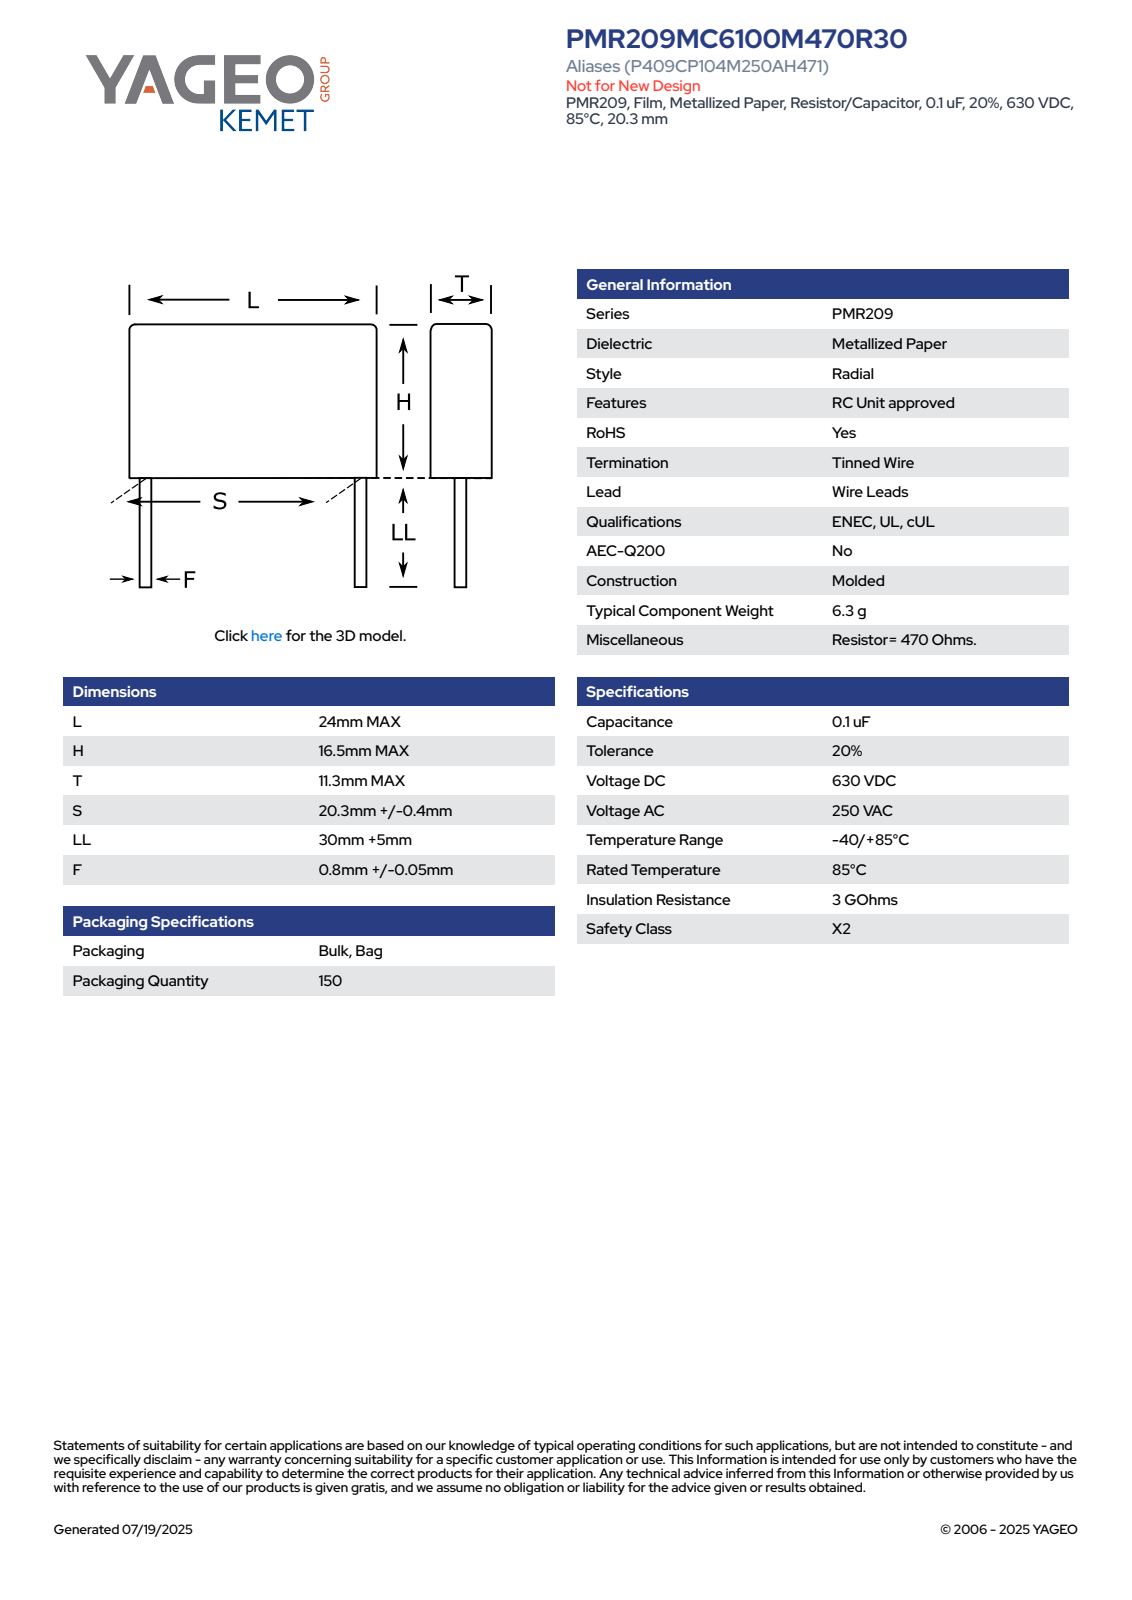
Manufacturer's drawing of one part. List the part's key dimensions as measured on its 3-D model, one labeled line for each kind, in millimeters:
Part name (STEP PRODUCT): CFR_MOLDED_24X16.5X11.3_L24H16.5T11.3S20.3LL35F0.85
STEP written by: SolidWorks 2014 (AUTOMOTIVE_DESIGN)
Units: millimetres
Bodies: 4 solids, 73 faces (65 planar, 8 cylindrical, 0 other)
Overall size (bounding box): 51.5 × 24 × 11.3
Volume: 4 511 mm³ · Surface area: 1 907 mm²
Round bosses / shafts (diameter × count): ⌀0.85 ×2
Partial cylindrical surfaces — rounded edges, fillets, slot ends (radius × count): R0.5 ×4
Main face-to-face distances: 11.3, 16.5, 24, 11.31, 35, 51.5, 44.07, 9.07, 7.43, 41.92
